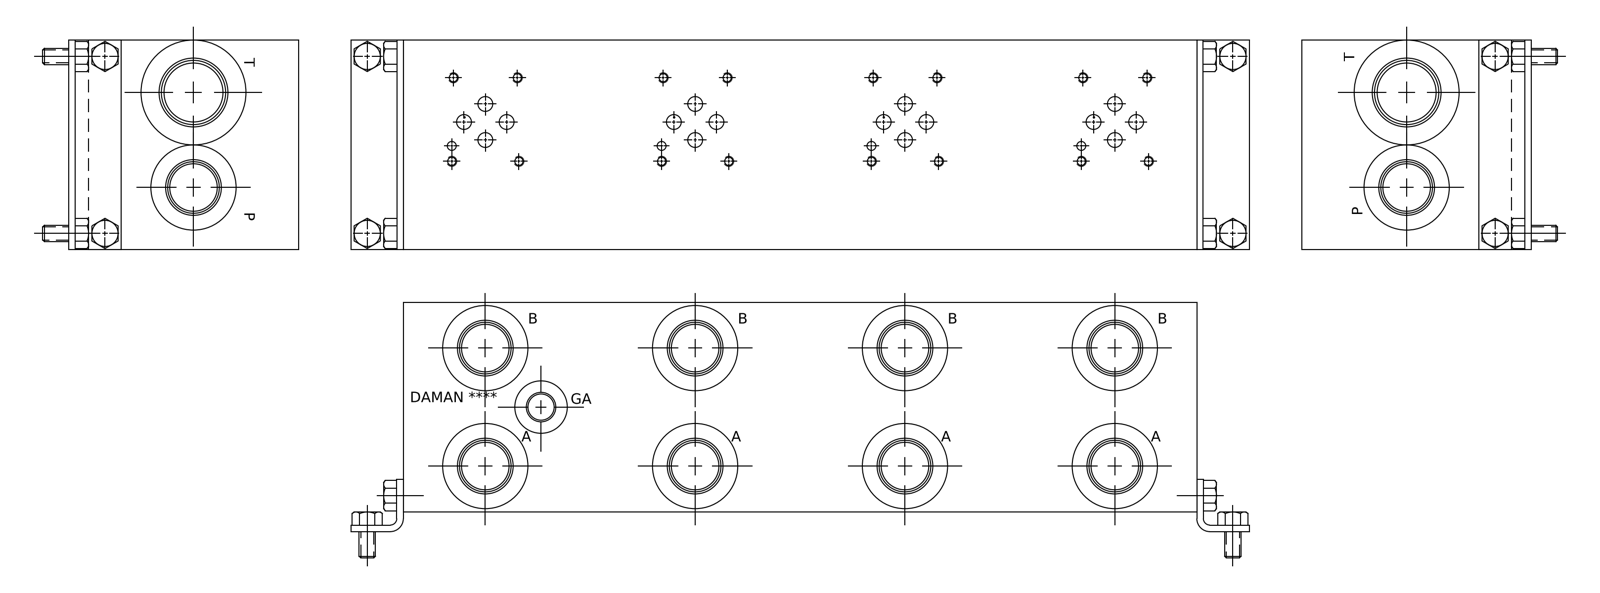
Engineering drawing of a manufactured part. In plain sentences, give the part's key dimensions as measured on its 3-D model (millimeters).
The part is named "Part_AD03HP044S_3D". Its 3-D file was written by "Autodesk Inventor 2020 (AUTOMOTIVE_DESIGN)". It is 1 solid with 836 faces: 450 planar, 125 cylindrical and 261 other. Overall it measures 384.18 by 101.6 by 101.6 millimeters. Its volume is 3 715 000 cubic millimeters and its surface area 216 704 square millimeters. Round holes: 16 of diameter 3.78, 16 of diameter 4.83, 12 of diameter 6.35, 9 of diameter 23.01, 9 of diameter 24.92, 9 of diameter 27.43, 9 of diameter 42.04, 5 of diameter 26.99, 4 of diameter 3.96, 4 of diameter 7.14, 4 of diameter 27, 2 of diameter 6.53. The main face-to-face distances are 101.6, 0.79, 384.18, 100.81, 383.39, 382.6, 19.05, 19.84, 81.76, 364.34. The hole center spacings are 101.6, 203.2, 304.8, 13.52, 13.54, 91.68, 91.71, 103.09.
